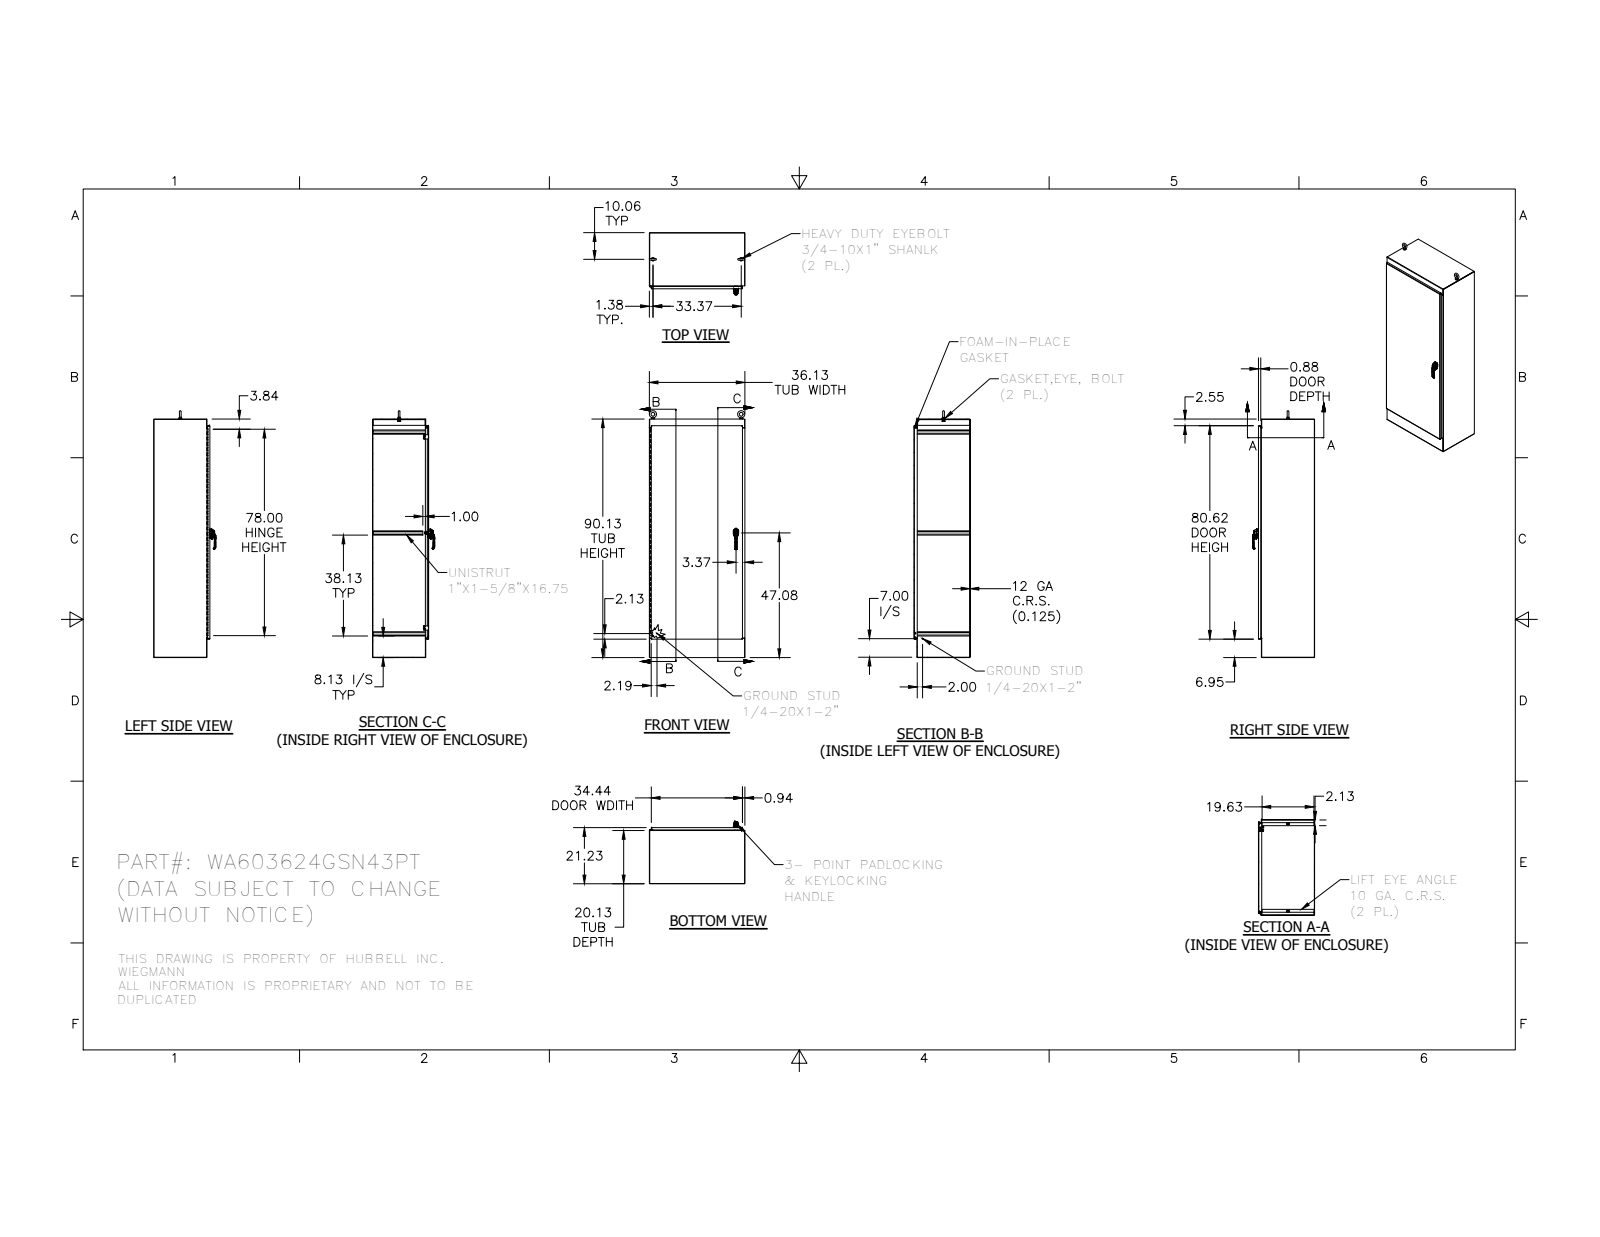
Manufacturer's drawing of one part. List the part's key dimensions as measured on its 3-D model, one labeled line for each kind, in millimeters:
Part name (STEP PRODUCT): WA9036FSN43PT-FIP; HFW31233; WA9036FSN43PTDR; HFW31712 (+8 more)
STEP written by: SolidWorks 2014 (AUTOMOTIVE_DESIGN)
Units: millimetres
Bodies: 52 solids, 1844 faces (833 planar, 691 cylindrical, 320 other)
Overall size (bounding box): 2368.5 × 917.6 × 539.2
Volume: 27 100 000 mm³ · Surface area: 17 230 000 mm²
Round holes (diameter × count): ⌀7 ×8, ⌀9.5 ×8, ⌀5.1 ×4, ⌀7.1 ×3, ⌀6.1 ×2, ⌀6.4 ×2, ⌀6.4 ×2, ⌀10.2 ×2, ⌀10.3 ×2, ⌀11.4 ×2, ⌀16.3 ×2, ⌀20.7 ×2
Round bosses / shafts (diameter × count): ⌀31.8 ×2, ⌀28.4 ×2, ⌀25.4 ×2, ⌀19.1 ×2, ⌀14.3 ×2, ⌀13.4 ×2, ⌀12.7 ×2, ⌀9.5 ×2
Partial cylindrical surfaces — rounded edges, fillets, slot ends (radius × count): R0.3 ×16, R3.2 ×16, R0.8 ×15, R4 ×15, R1.3 ×14, R0.5 ×12, R1.3 ×12, R2.2 ×12
Main face-to-face distances: 3.2, 914.4, 3.2, 532.9, 536.1, 539.2, 536, 911.2, 917.6, 2286
Hole centre spacings: 220.1, 660.4, 440.3, 880.5, 1825.8, 1844.9, 19.4, 19.4
